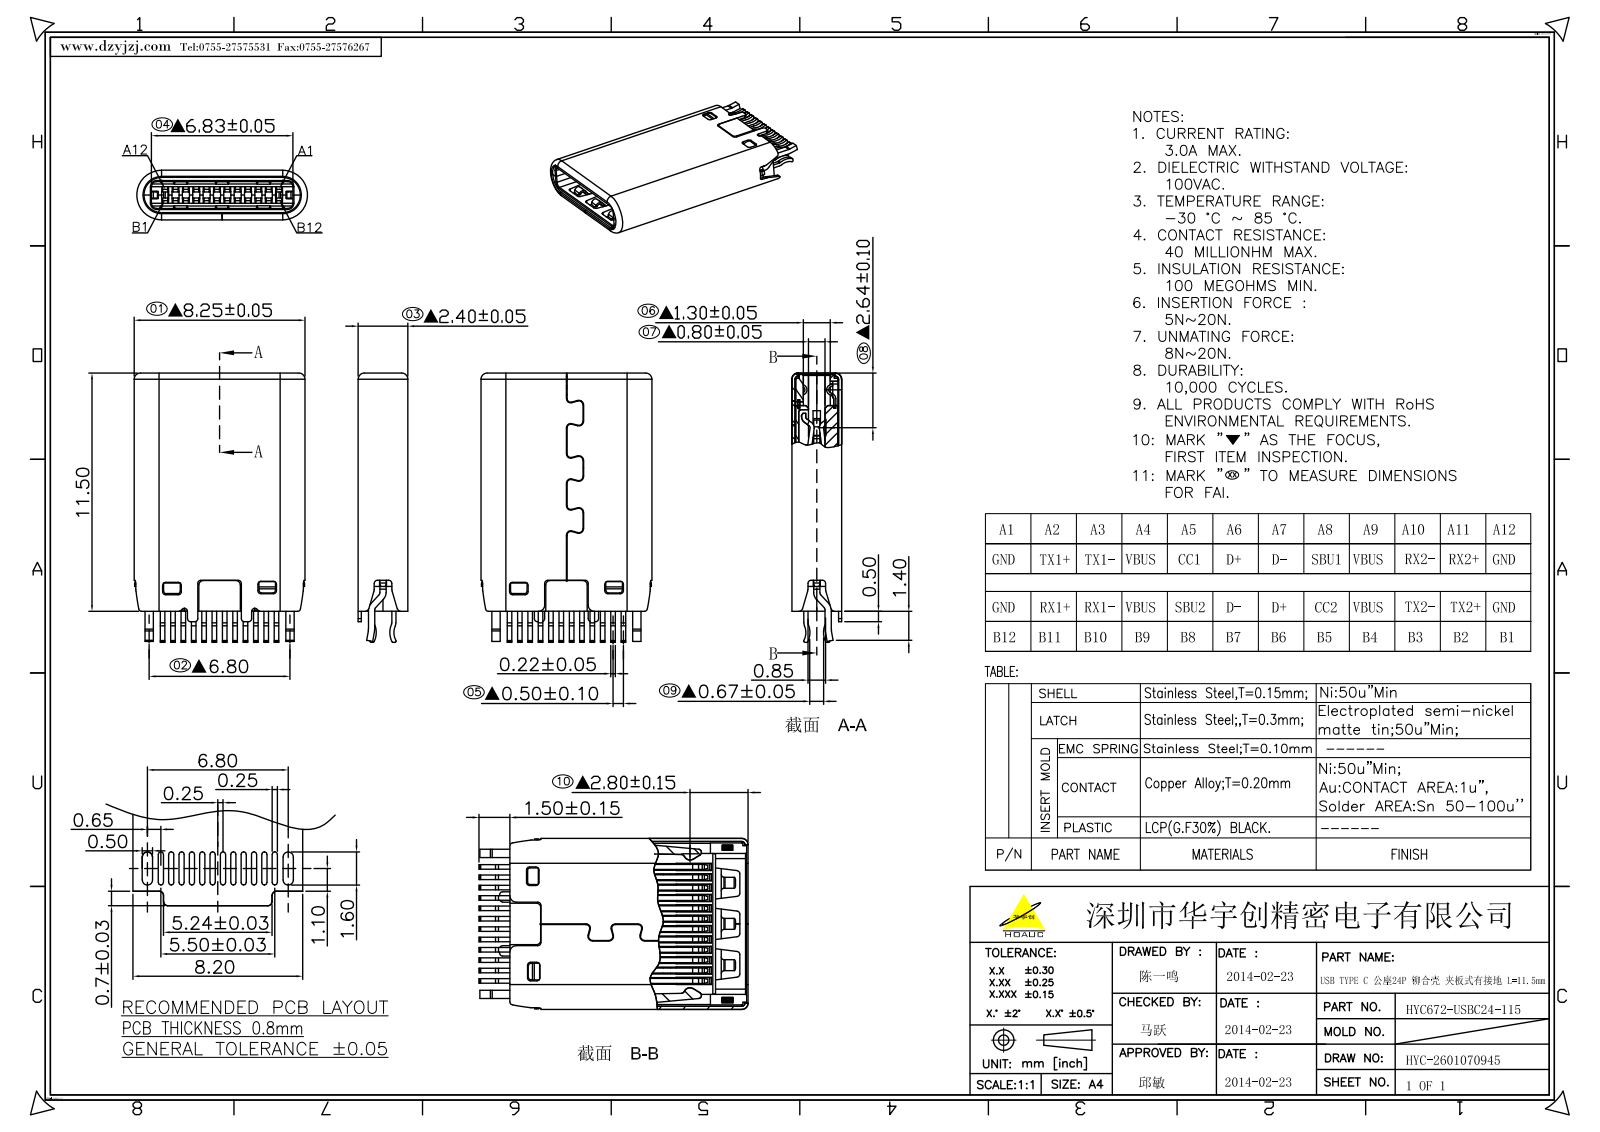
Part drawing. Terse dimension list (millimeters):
name: TANPIAN-PLASTIC_1_2__2_30_1_1_2
written by: CREO PARAMETRIC BY PTC INC, 2025010 (AUTOMOTIVE_DESIGN)
unit: mm
bodies: 1 solid, 1035 faces (686 planar, 337 cylindrical, 12 other)
size: 13.01 × 8.25 × 2.42
volume: 170 mm³; area: 538 mm²
holes: 3× ⌀1, 2× ⌀0.6
bosses: 1× ⌀1
rounds: 57× R0.15, 24× R0.13, 10× R0.2, 10× R0.3, 6× R0.25, 6× R1.05, 3× R0.1, 2× R0.18
face distances: 2.4, 0.79, 0.81, 0.8, 0.57, 1.61, 1.59, 1.06, 1.34, 0.53
hole spacings: 3.15, 5.32, 1.28, 1.9, 4, 4.43, 4.48, 4.6
